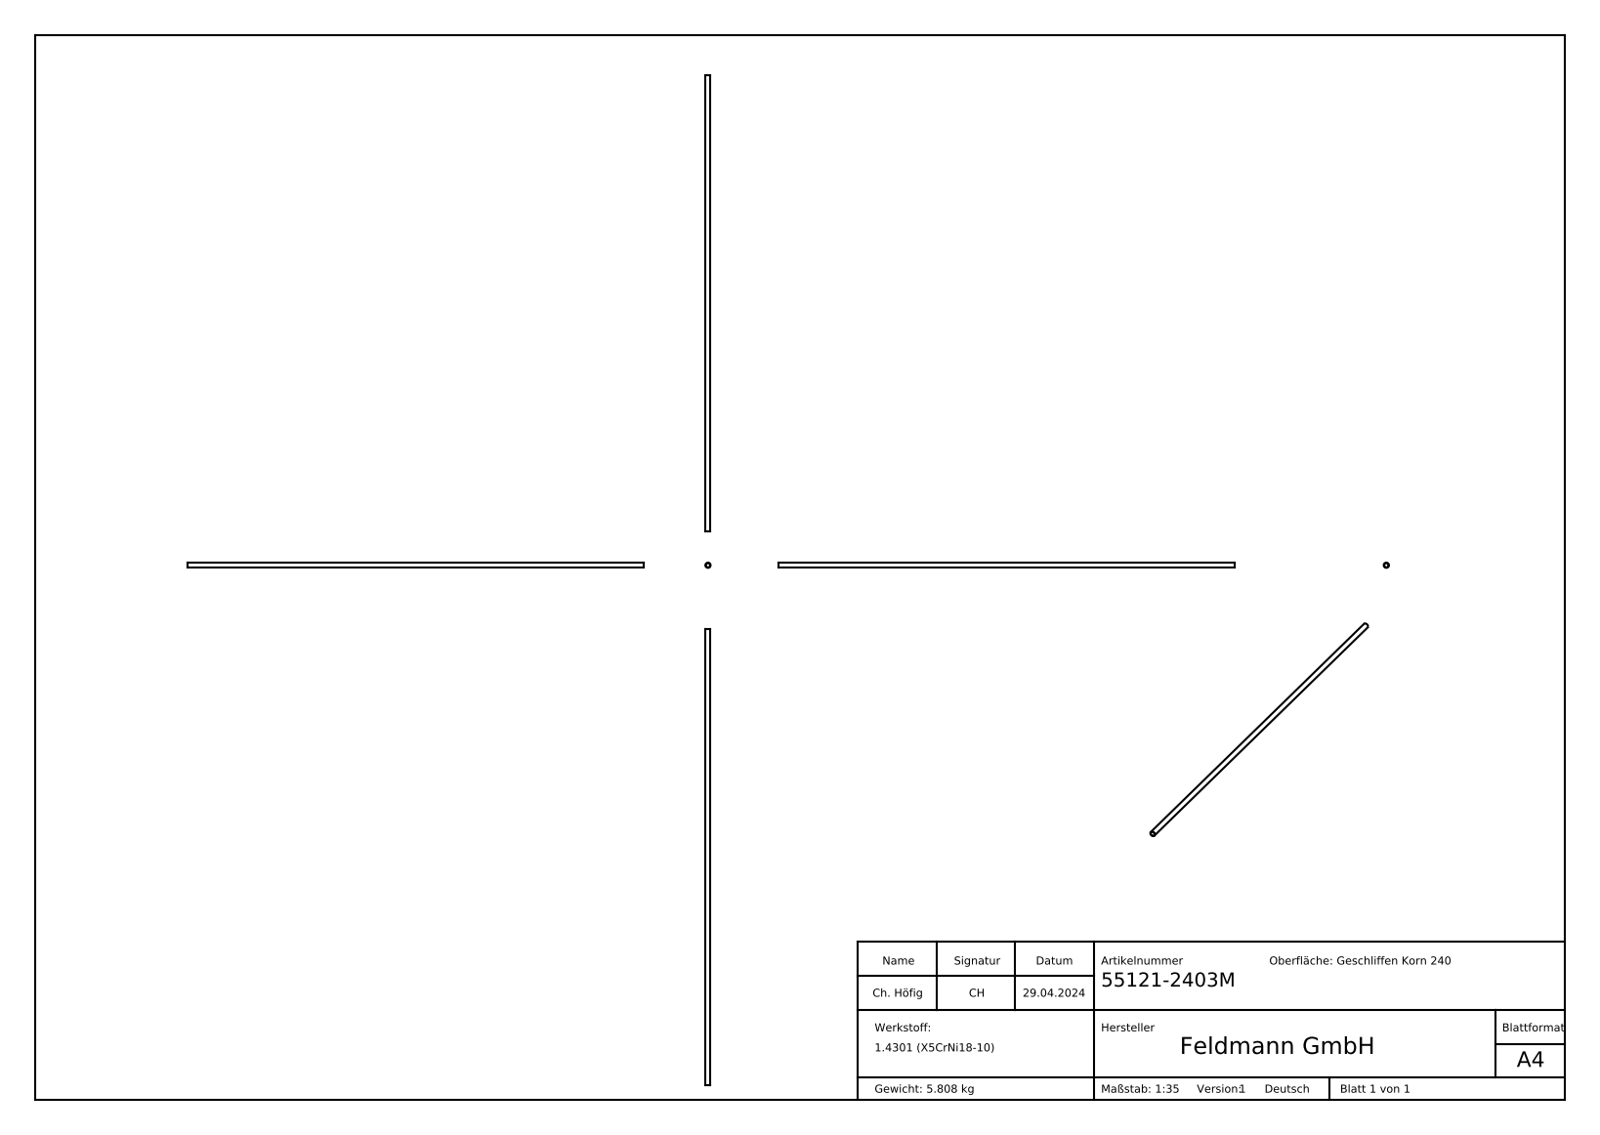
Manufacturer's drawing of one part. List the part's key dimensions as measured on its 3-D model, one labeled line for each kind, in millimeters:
Part name (STEP PRODUCT): 55121-2403M
STEP written by: SolidWorks 2018 (CONFIG_CONTROL_DESIGN)
Units: millimetres
Bodies: 1 solid, 293 faces (147 planar, 27 cylindrical, 119 other)
Overall size (bounding box): 3000 × 33.7 × 33.7
Volume: 735 132 mm³ · Surface area: 588 604 mm²
Round holes (diameter × count): ⌀28.7 ×1
Round bosses / shafts (diameter × count): ⌀33.7 ×1
Partial cylindrical surfaces — rounded edges, fillets, slot ends (radius × count): R14.45 ×1
Main face-to-face distances: 3000, 0.71, 1.57, 2.24, 1.13, 0.64, 2.41, 0.79, 0.73, 0.63
